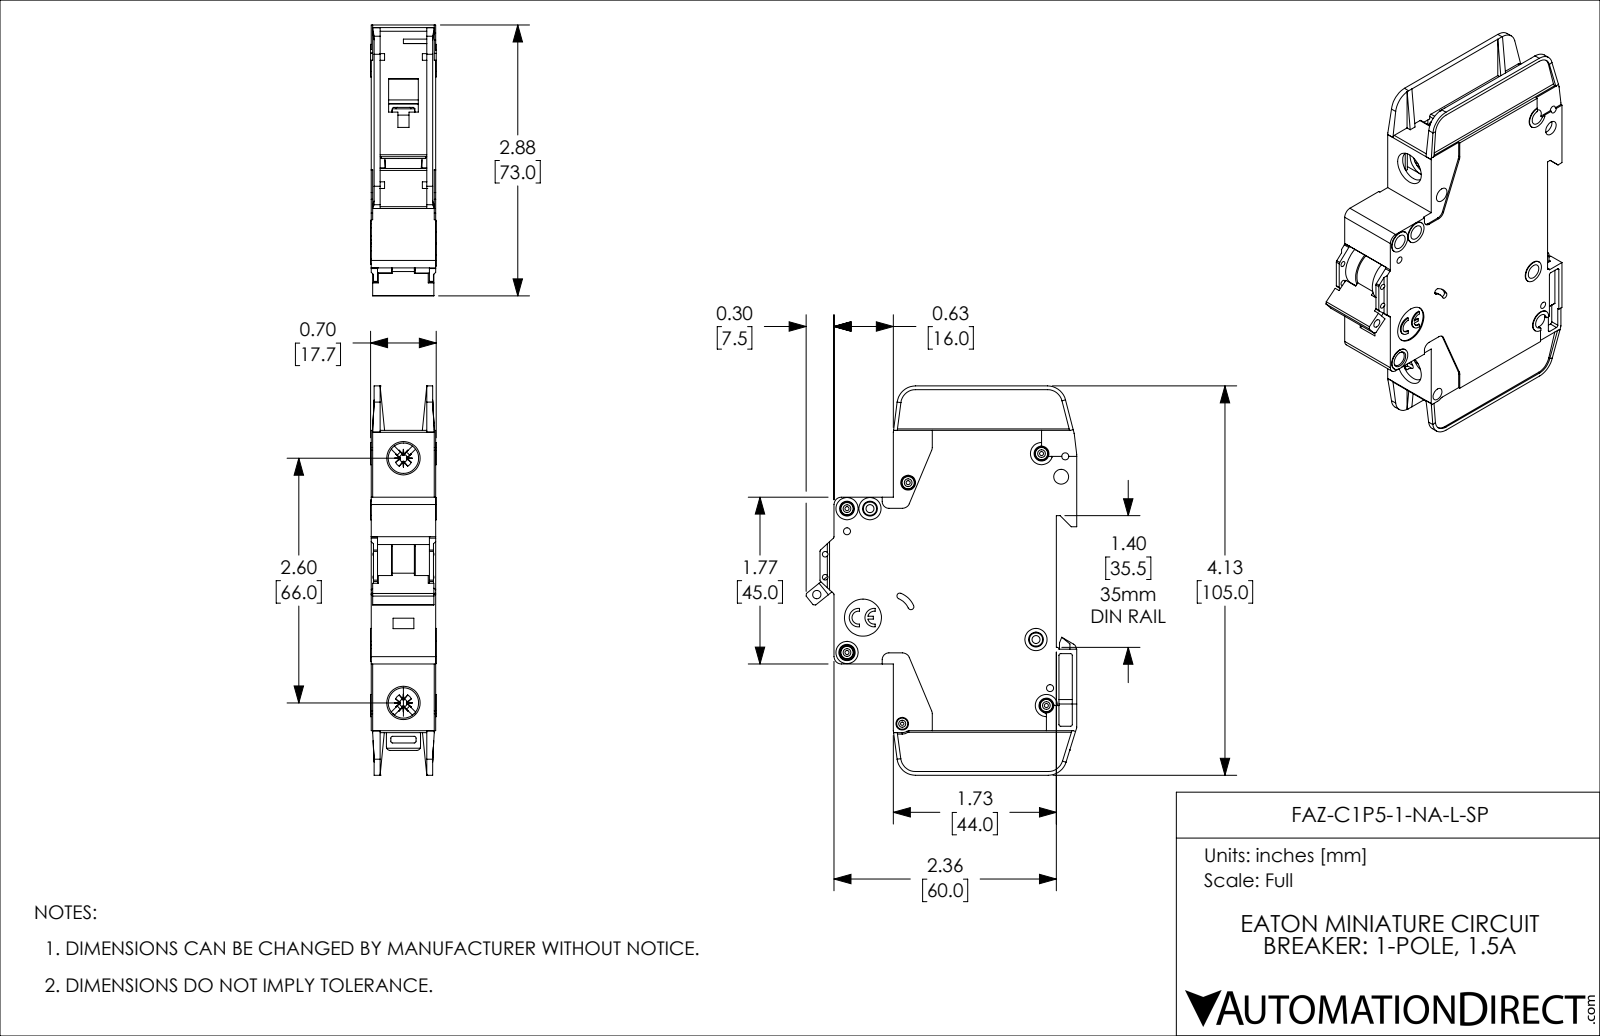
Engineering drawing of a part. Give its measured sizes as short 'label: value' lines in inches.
name: FAZ-C1P5-1-NA-L-SP
written by: SolidWorks 2019 (AUTOMOTIVE_DESIGN)
unit: in
bodies: 1 solid, 1127 faces (671 planar, 357 cylindrical, 99 other)
size: 4.134 × 2.876 × 0.697
volume: 4.682 in³; area: 41.01 in²
holes: 8× ⌀0.157, 5× ⌀0.043, 4× ⌀0.075, 2× ⌀0.059, 2× ⌀0.085, 2× ⌀0.323, 1× ⌀0.035, 1× ⌀0.089, 1× ⌀0.098, 1× ⌀0.134, 1× ⌀0.394
bosses: 5× ⌀0.13, 4× ⌀0.236, 2× ⌀0.118, 1× ⌀0.098
rounds: 42× R0.02, 10× R0.016, 10× R0.039, 8× R0.079, 5× R0.197, 4× R0.008, 4× R0.026, 4× R0.043
face distances: 0.047, 0.685, 0.591, 0.638, 0.094, 0.543, 0.016, 0.031, 0.496, 0.575
hole spacings: 0.244, 0.537, 0.87, 0.189, 0.199, 0.204, 0.221, 0.24
